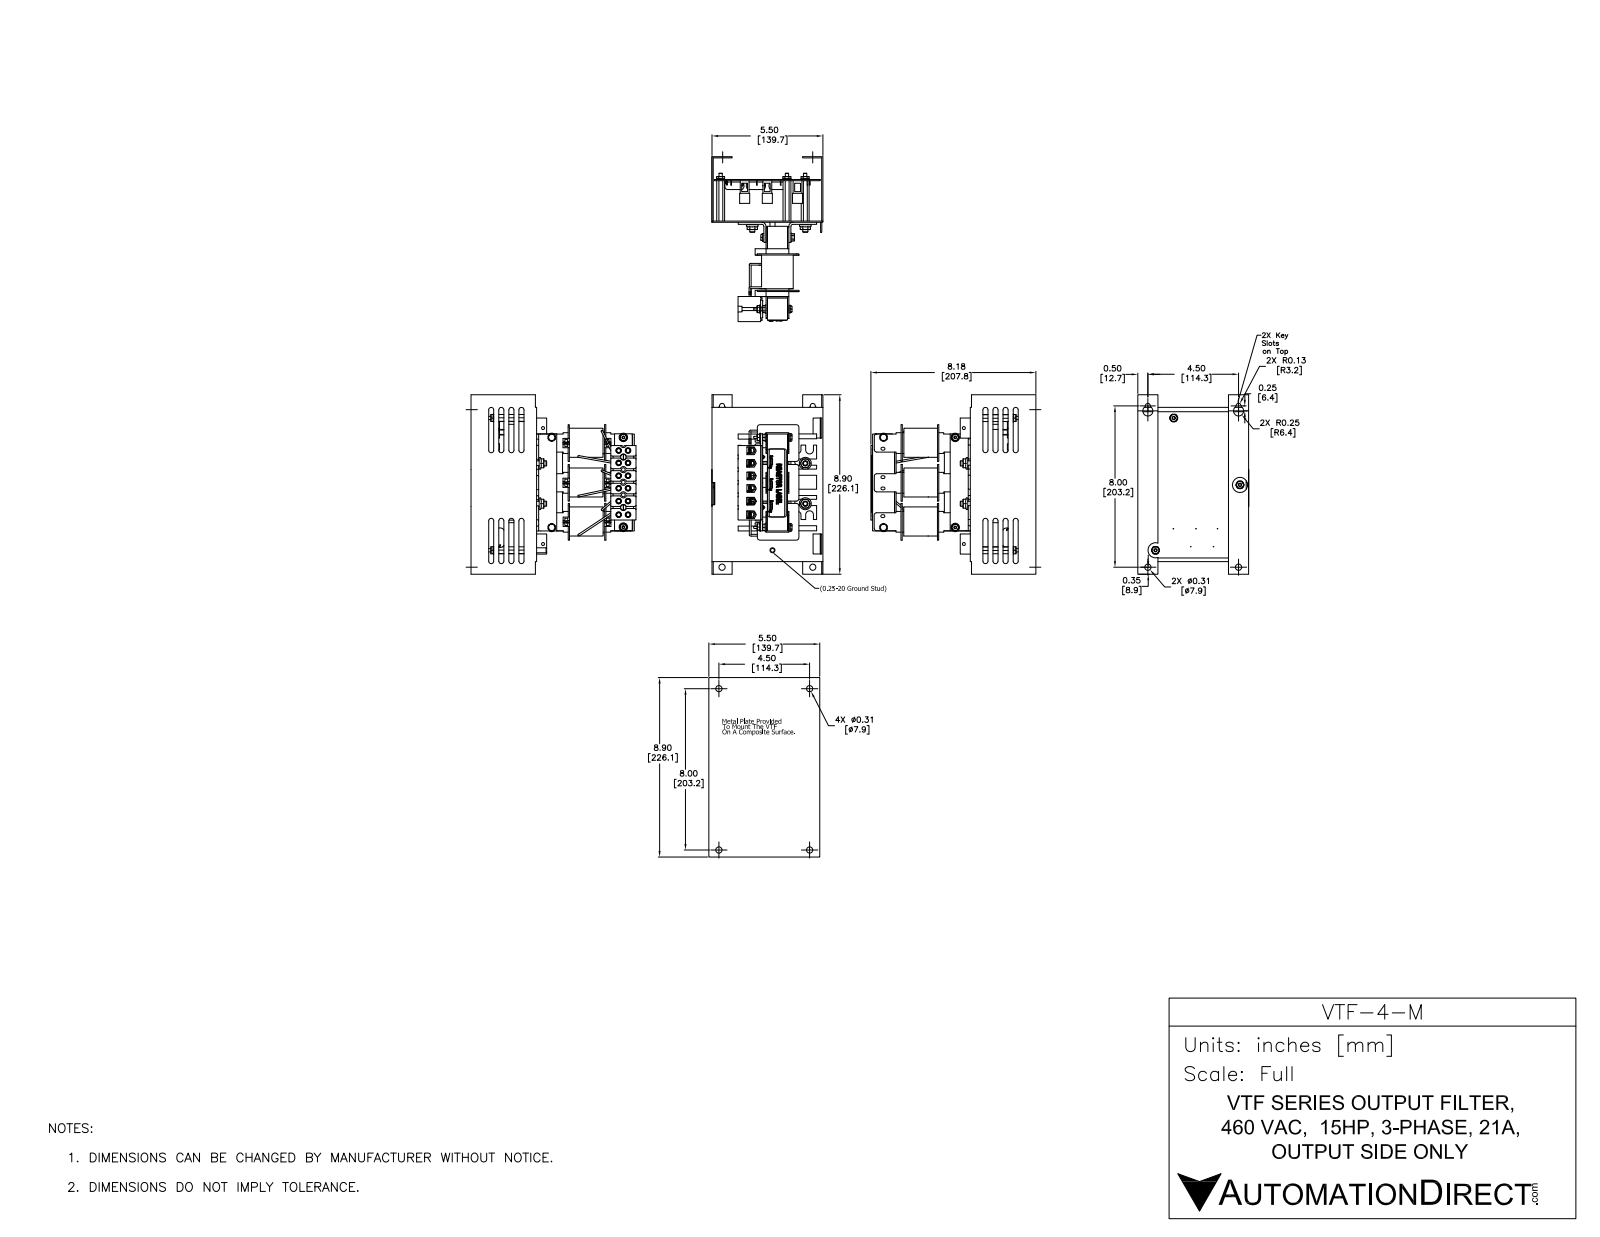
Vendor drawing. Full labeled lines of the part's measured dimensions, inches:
Part name (STEP PRODUCT): VTF 16A-27A r1 comb1
STEP written by: SolidWorks 2017 (AUTOMOTIVE_DESIGN)
Units: inches
Bodies: 56 solids, 3938 faces (2110 planar, 1153 cylindrical, 675 other)
Overall size (bounding box): 8.9 × 8.18 × 5.505
Volume: 45.6 in³ · Surface area: 733.5 in²
Round holes (diameter × count): ⌀0.276 ×16, ⌀0.31 ×7, ⌀0.03 ×6, ⌀0.14 ×6, ⌀0.177 ×6, ⌀0.104 ×5, ⌀0.186 ×5, ⌀0.16 ×4, ⌀0.164 ×3, ⌀0.22 ×3, ⌀0.15 ×2, ⌀0.19 ×2
Round bosses / shafts (diameter × count): ⌀0.03 ×18, ⌀0.25 ×17, ⌀0.26 ×12, ⌀0.204 ×12, ⌀0.088 ×12, ⌀0.088 ×6, ⌀0.38 ×4, ⌀0.375 ×2
Partial cylindrical surfaces — rounded edges, fillets, slot ends (radius × count): R0.03 ×44, R0.125 ×36, R0.012 ×31, R0.029 ×24, R0.039 ×24, R0.049 ×24, R0.05 ×20, R0.076 ×18
Main face-to-face distances: 0.059, 0.065, 5.441, 2, 1.065, 2.063, 0.063, 2.059, 2.122, 3.191
Hole centre spacings: 0.465, 3.555, 1.24, 1.25, 1.328, 1.939, 0.378, 0.381
